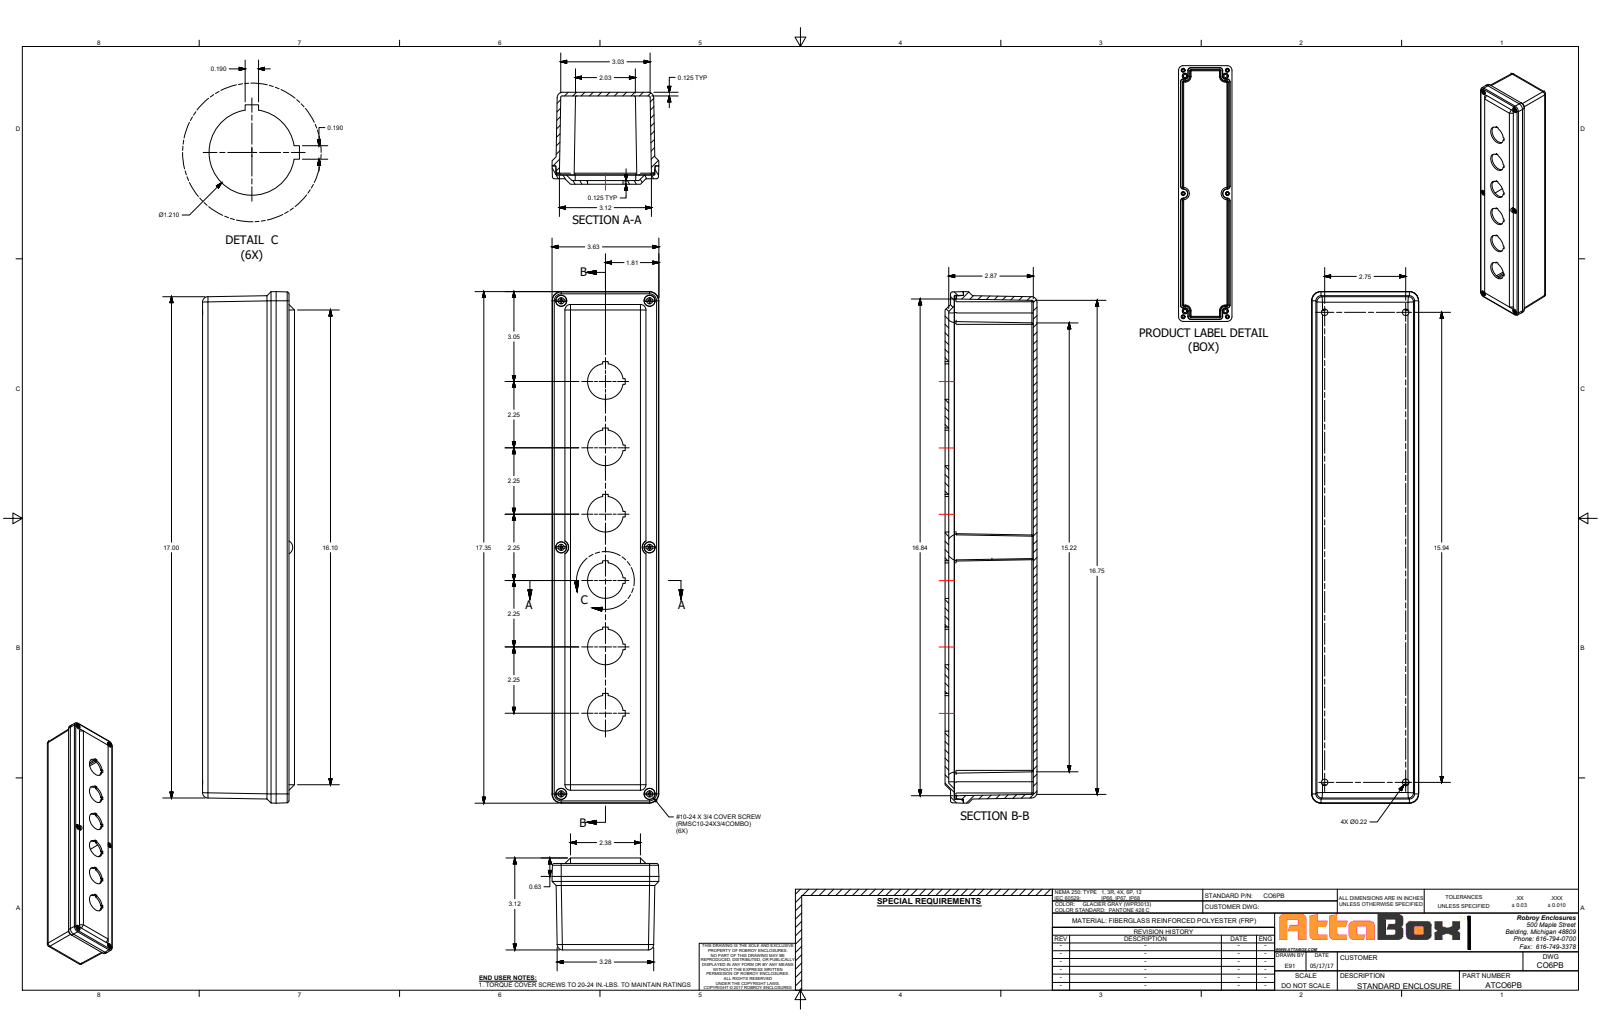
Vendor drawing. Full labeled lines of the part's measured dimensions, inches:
Part name (STEP PRODUCT): CO6PB
STEP written by: SolidWorks 2018 (AUTOMOTIVE_DESIGN)
Units: inches
Bodies: 15 solids, 551 faces (261 planar, 160 cylindrical, 130 other)
Overall size (bounding box): 17.346 × 3.625 × 3.12
Volume: 34.17 in³ · Surface area: 516 in²
Round holes (diameter × count): ⌀0.219 ×8, ⌀0.159 ×6, ⌀0.19 ×6, ⌀1.21 ×6, ⌀0.375 ×4, ⌀0.217 ×2, ⌀0.375 ×2
Round bosses / shafts (diameter × count): ⌀0.371 ×6, ⌀0.27 ×6, ⌀0.177 ×6, ⌀0.44 ×2
Partial cylindrical surfaces — rounded edges, fillets, slot ends (radius × count): R0.012 ×24, R0.031 ×20, R0.048 ×8, R0.063 ×4, R0.176 ×4, R0.22 ×4, R0.312 ×4, R0.325 ×4
Main face-to-face distances: 0.125, 0.122, 2.995, 3.12, 2.87, 2.807, 0.187, 0.313, 0.062, 0.125
Hole centre spacings: 2.25, 0.411, 2.717, 2.901, 3.693, 4.5, 7.97, 8.361
